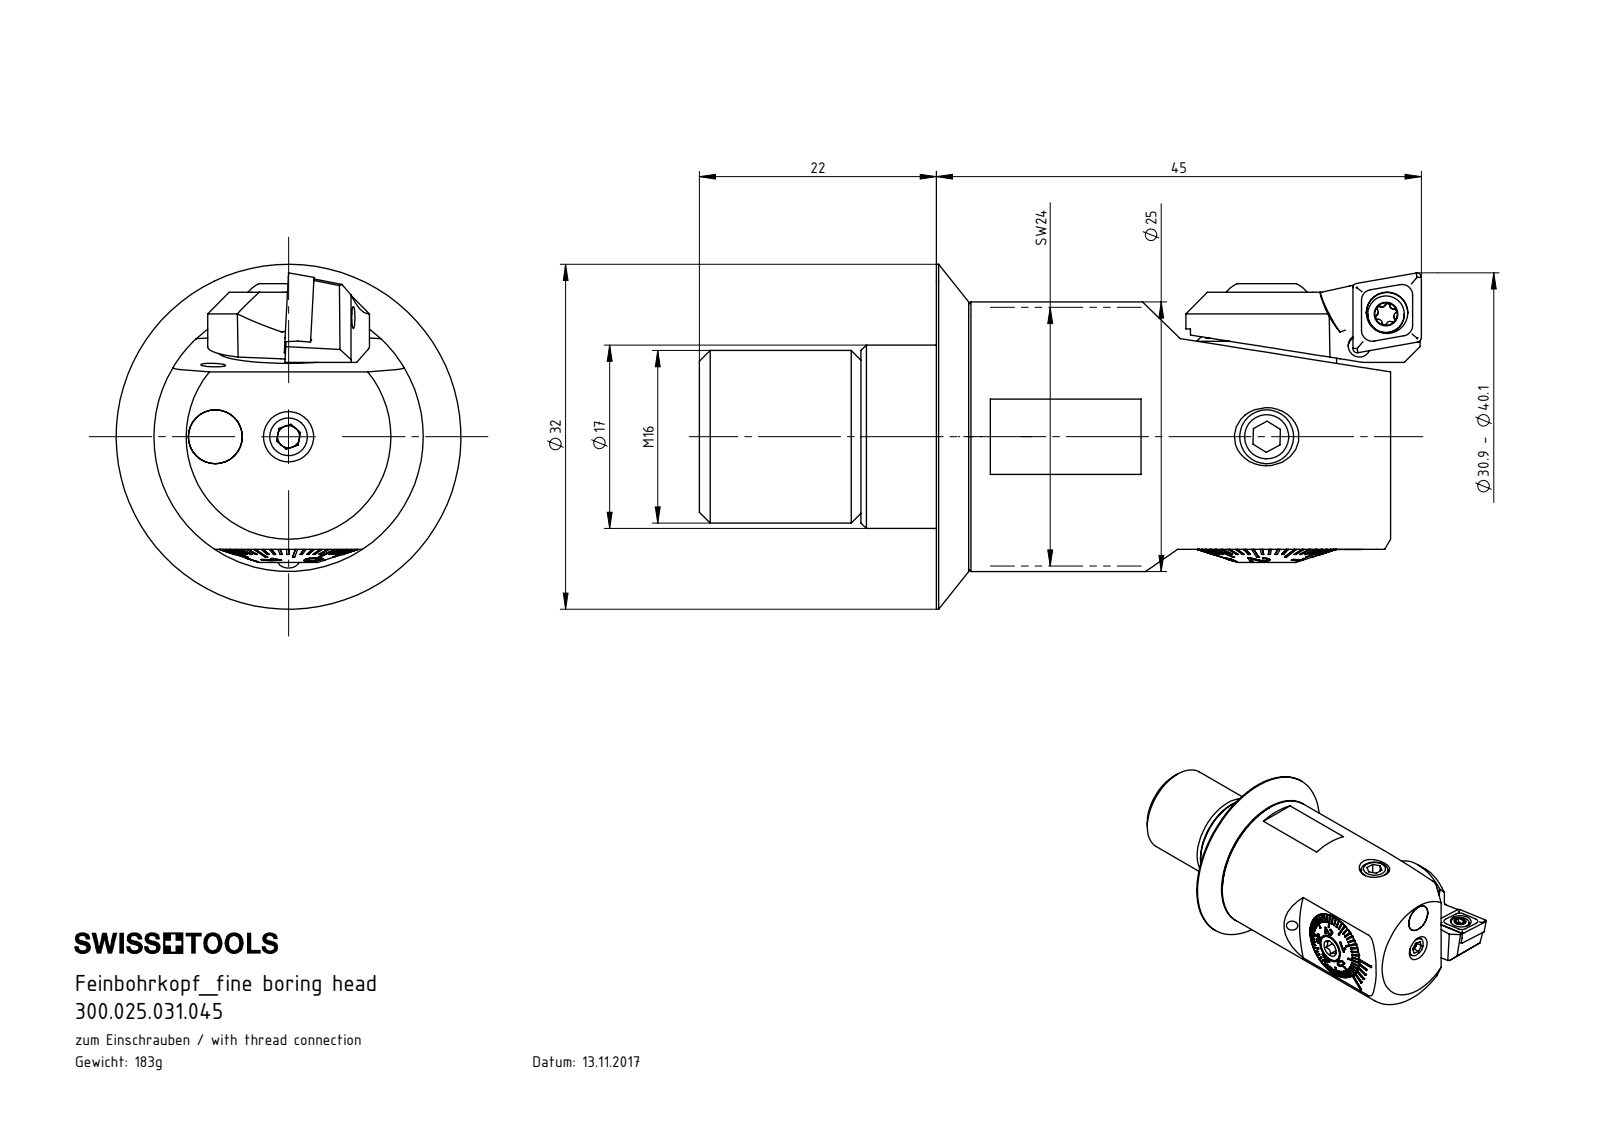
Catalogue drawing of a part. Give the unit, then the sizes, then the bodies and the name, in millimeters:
Units: millimetres
Overall size (bounding box): 67 × 32 × 32
Round holes (diameter × count): ⌀2 ×5, ⌀2.05 ×2, ⌀4.2 ×2, ⌀2.1 ×1, ⌀2.4 ×1, ⌀2.7 ×1, ⌀2.8 ×1, ⌀3 ×1, ⌀3.3 ×1, ⌀3.85 ×1, ⌀5 ×1, ⌀5.5 ×1
Round bosses / shafts (diameter × count): ⌀5 ×2, ⌀4.95 ×2, ⌀2.5 ×2, ⌀32 ×1, ⌀25 ×1, ⌀16 ×1, ⌀12.98 ×1, ⌀12.85 ×1
Partial cylindrical surfaces — rounded edges, fillets, slot ends (radius × count): R0.21 ×6, R0.36 ×5, R0.5 ×4, R1.32 ×2, R0.2 ×1, R0.36 ×1, R1.25 ×1, R2 ×1
Main face-to-face distances: 3, 42.15, 39.15, 8, 1.5, 15, 3.1, 15.7, 0.8, 19.6
Hole centre spacings: 3.84, 3.99, 4.48, 6.8, 9.46, 16.65
Volume: 23 247 mm³ · Surface area: 14 677 mm²
Bodies: 18 solids, 649 faces (357 planar, 84 cylindrical, 208 other)
Part name (STEP PRODUCT): F25-WCA.001.006_D_fertigbearbeitet; HP5-F25.031.045_A; ISO 4026 - M5 x 4_PreviewCfg; D32-D25.HP5.003_A (+8 more)
STEP written by: SolidWorks 2017 (AUTOMOTIVE_DESIGN)
